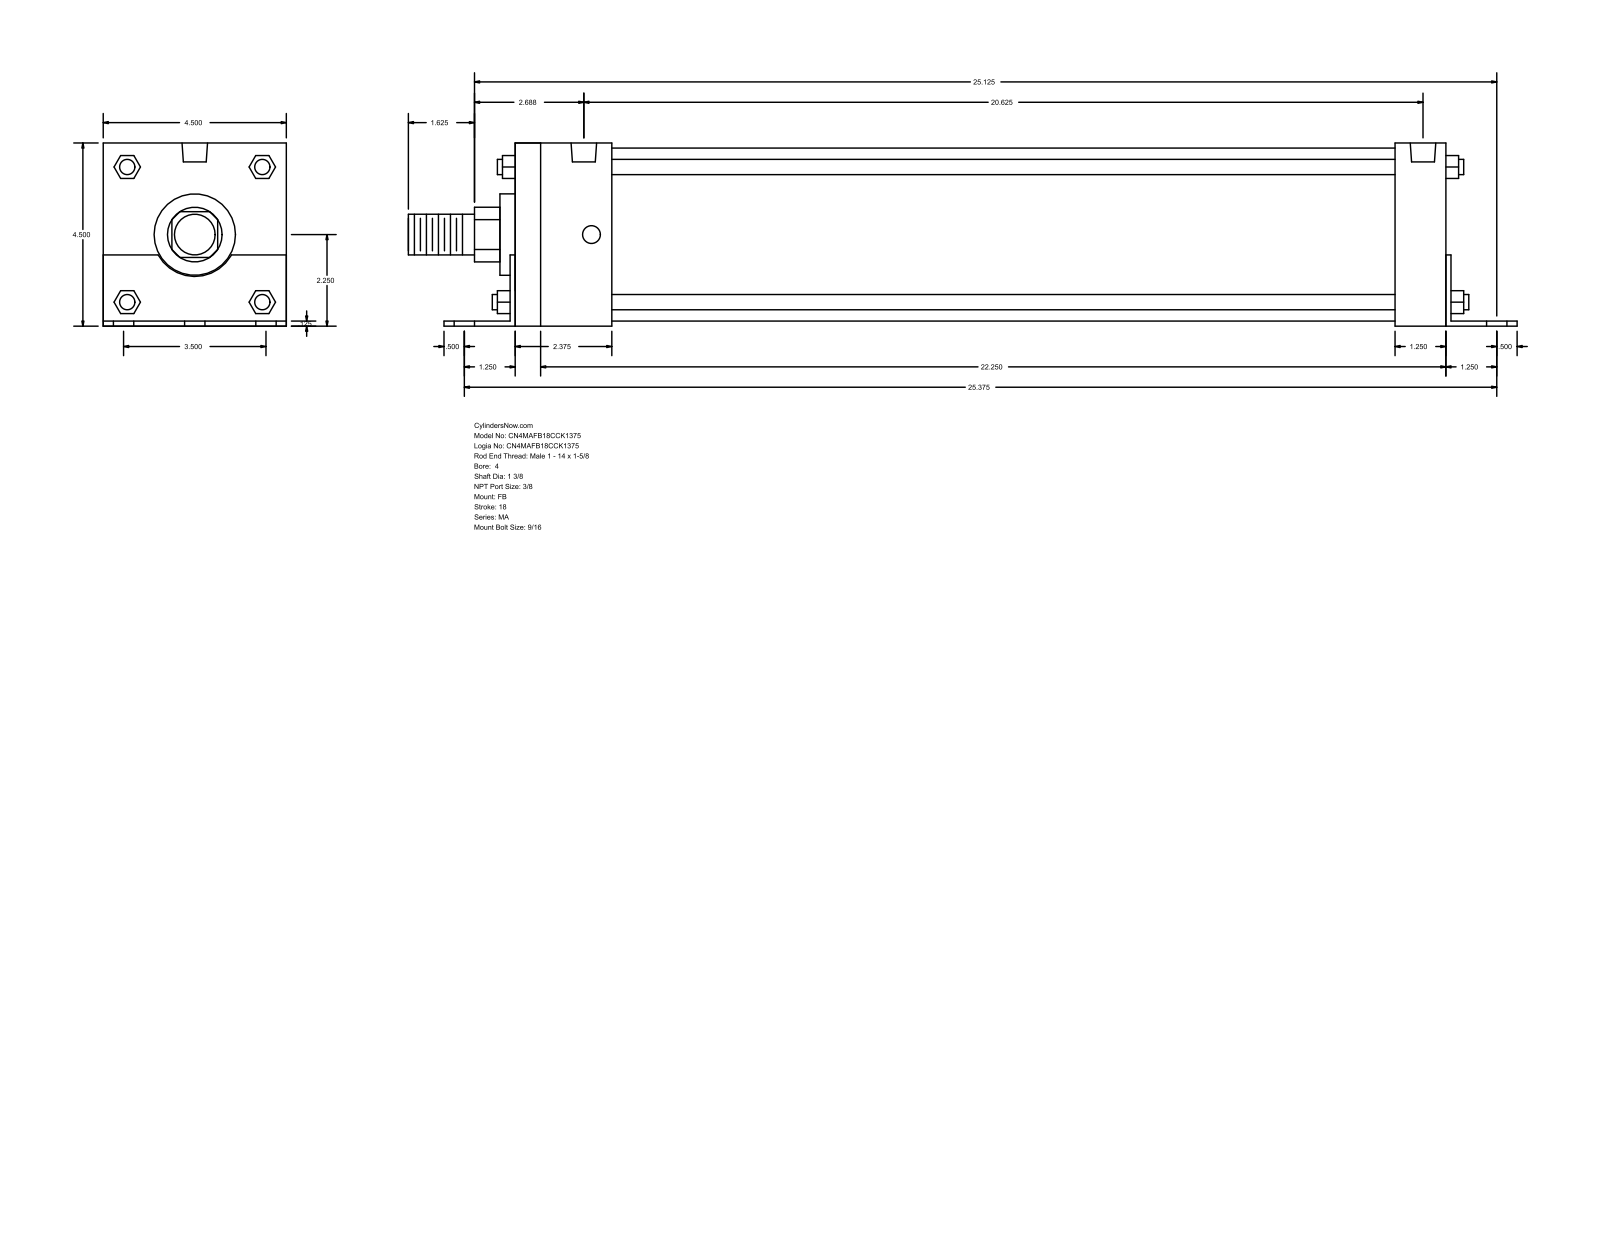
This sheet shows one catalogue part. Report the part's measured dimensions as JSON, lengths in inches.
{"part_name": "MA_FB__0400_1.375", "step_written_by": "GSSL Pune (CONFIG_CONTROL_DESIGN)", "units": "inches", "bodies": {"solids": 0, "faces": 140, "planar": 105, "cylindrical": 35, "other": 0}, "overall_size": [27.25, 4.502, 4.5], "round_holes": [[0.563, 6], [0.437, 4], [0.627, 2]], "round_bosses_or_shafts": [[0.375, 4], [4.25, 1], [2, 1], [1.375, 1], [1, 1]], "partial_cylinders_radius": [[0.672, 1], [1.03, 1]], "face_to_face_distances": [4.5, 0.125, 4.502, 0.123, 4.377, 22.875, 0.125, 23, 1.375, 23], "hole_center_spacings": [1.75, 25.435, 25.375, 2.519, 2.657, 3.419, 3.5, 3.582]}
